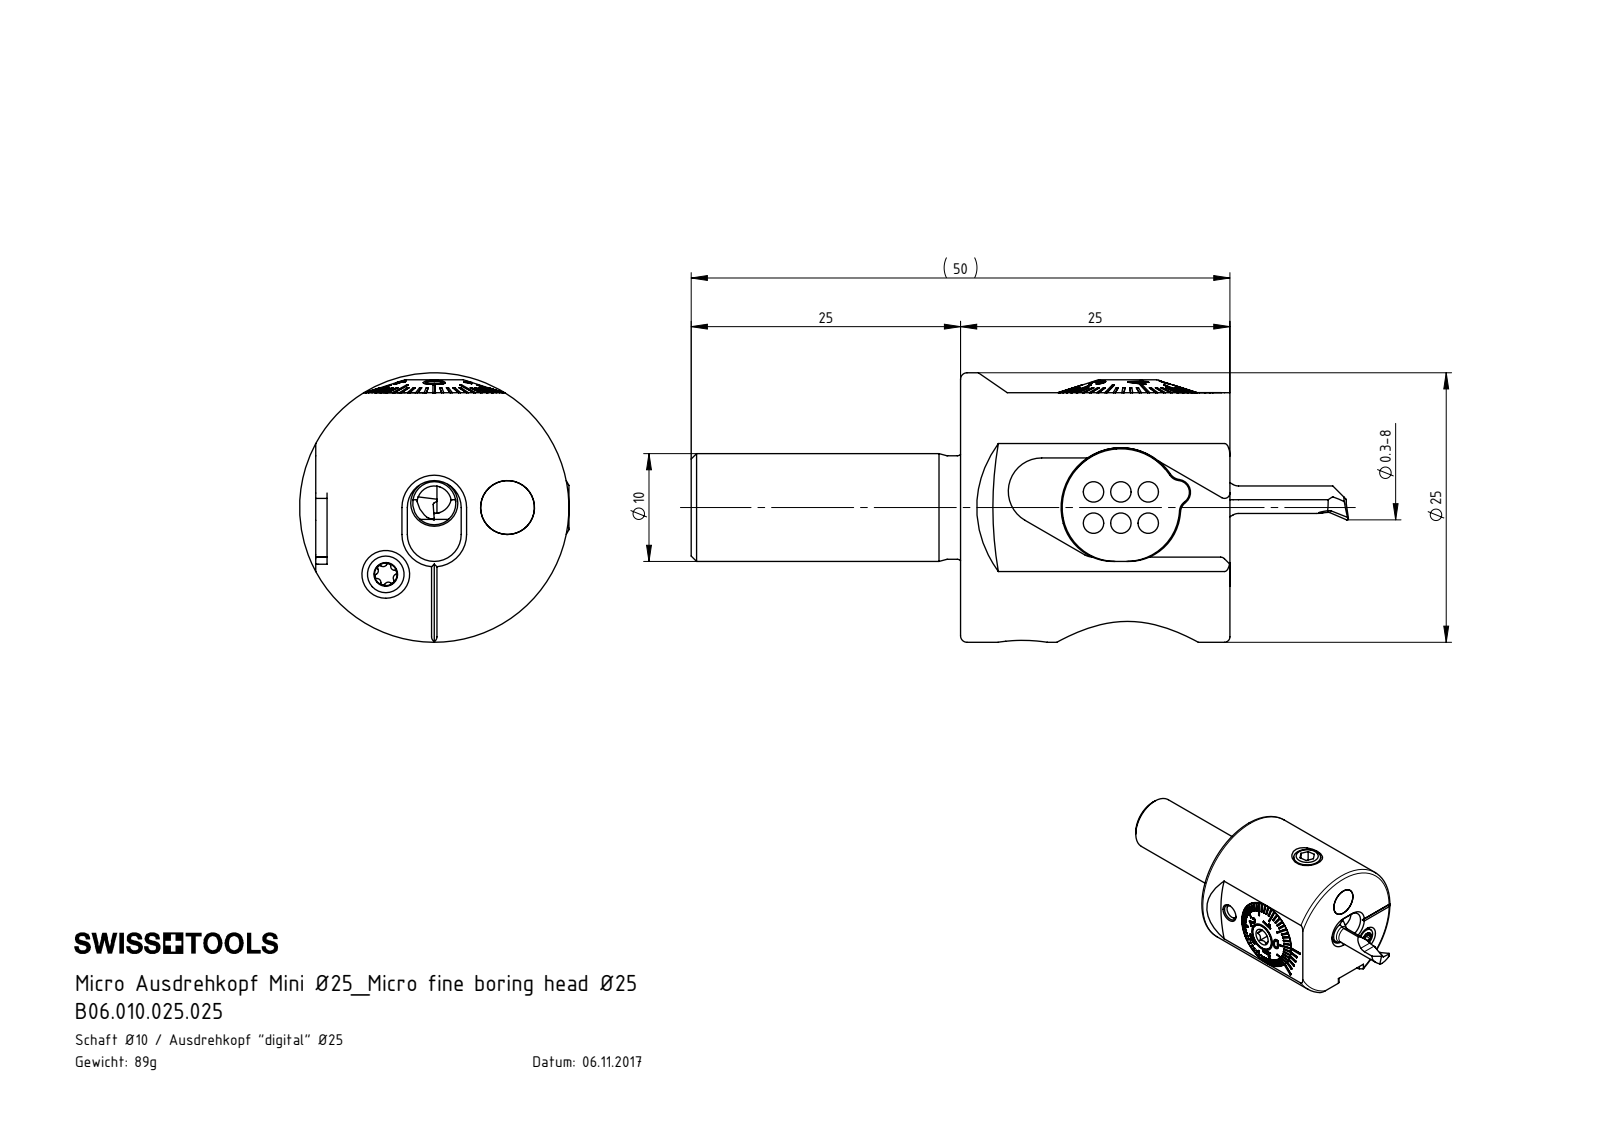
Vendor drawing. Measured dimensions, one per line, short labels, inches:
name: Klebstoff D5; Axx-BG4.003.xxx_A_A25; WCA-ER2.001.006_A; Mini_Schaft_4 (+8 more)
written by: SolidWorks 2017 (CONFIG_CONTROL_DESIGN)
unit: in
bodies: 18 solids, 835 faces (364 planar, 180 cylindrical, 291 other)
size: 2.402 × 0.984 × 0.984
volume: 0.721 in³; area: 15.54 in²
holes: 4× ⌀0.13, 4× ⌀0.197, 2× ⌀0.079, 1× ⌀0.028, 1× ⌀0.039, 1× ⌀0.094, 1× ⌀0.106, 1× ⌀0.118, 1× ⌀0.157, 1× ⌀0.165, 1× ⌀0.266, 1× ⌀0.287
bosses: 6× ⌀0.075, 3× ⌀0.157, 2× ⌀0.195, 1× ⌀0.984, 1× ⌀0.512, 1× ⌀0.511, 1× ⌀0.506, 1× ⌀0.419
rounds: 6× R0.008, 5× R0.014, 4× R0.008, 4× R0.087, 3× R0.02, 3× R0.043, 3× R0.047, 3× R0.063
face distances: 0.984, 0.154, 0.059, 0.031, 0.122, 0.063, 0.15, 0.091, 0.118, 0.053
hole spacings: 0.138, 0.216, 0.364, 0.016, 0.027, 0.102, 0.103, 0.246
